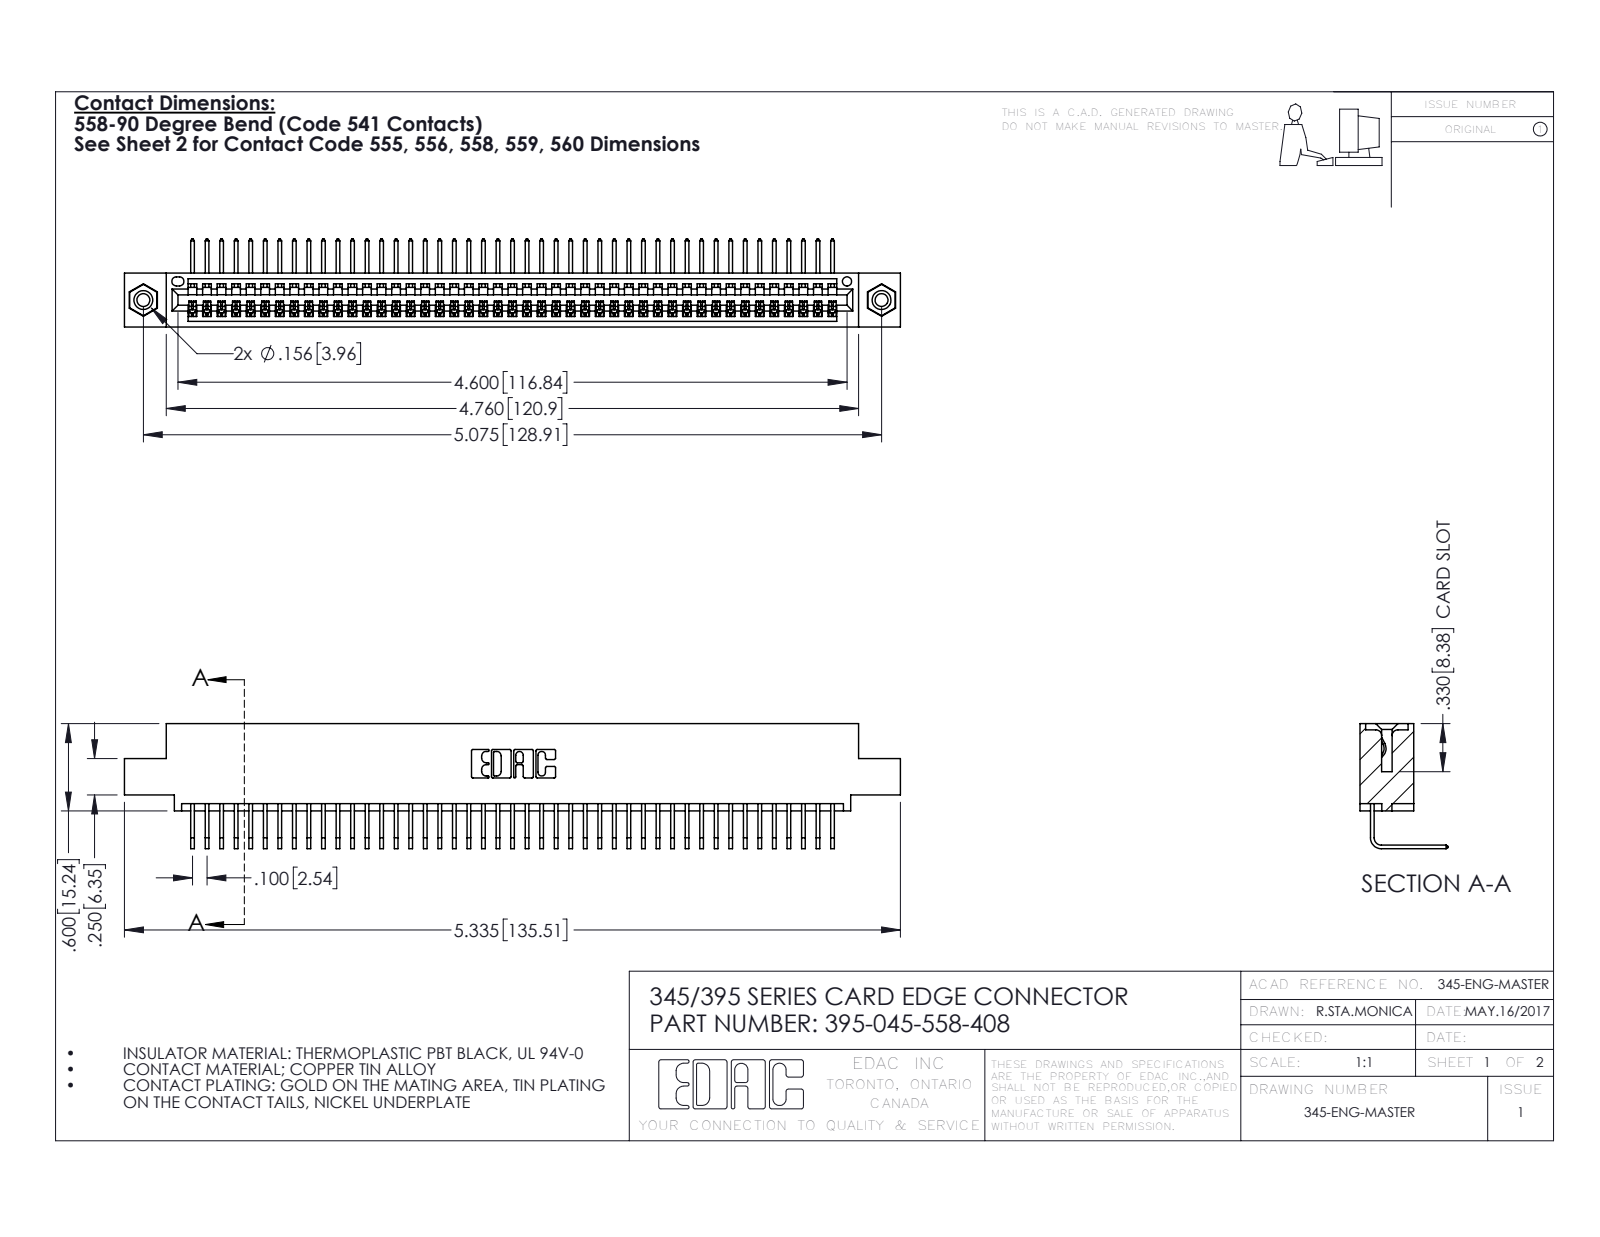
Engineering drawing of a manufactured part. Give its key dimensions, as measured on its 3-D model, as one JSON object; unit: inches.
{"part_name": "345-292-001_558 Tail - 2; 395-045-558-408; 345 Part_0.110 Offset - 0.156 Dia-TI; 345-250-001_345-250-003-102", "step_written_by": "SolidWorks 2016 (CONFIG_CONTROL_DESIGN)", "units": "inches", "bodies": {"solids": 48, "faces": 2890, "planar": 2006, "cylindrical": 868, "other": 16}, "overall_size": [5.335, 0.859, 0.605], "volume_in3": 0.791, "surface_area_in2": 28.29, "round_holes": [[0.089, 2], [0.125, 2], [0.156, 2], [0.064, 1]], "round_bosses_or_shafts": [[0.155, 2]], "partial_cylinders_radius": [[0.006, 90], [0.01, 22], [0.007, 6], [0.031, 6], [0.026, 3], [0.031, 2], [0.04, 2], [0.014, 1]], "face_to_face_distances": [0.072, 0.298, 0.37, 0.2, 0.098, 0.272, 0.025, 0.225, 0.149, 0.072], "hole_center_spacings": [0.27, 4.839, 5.075]}
